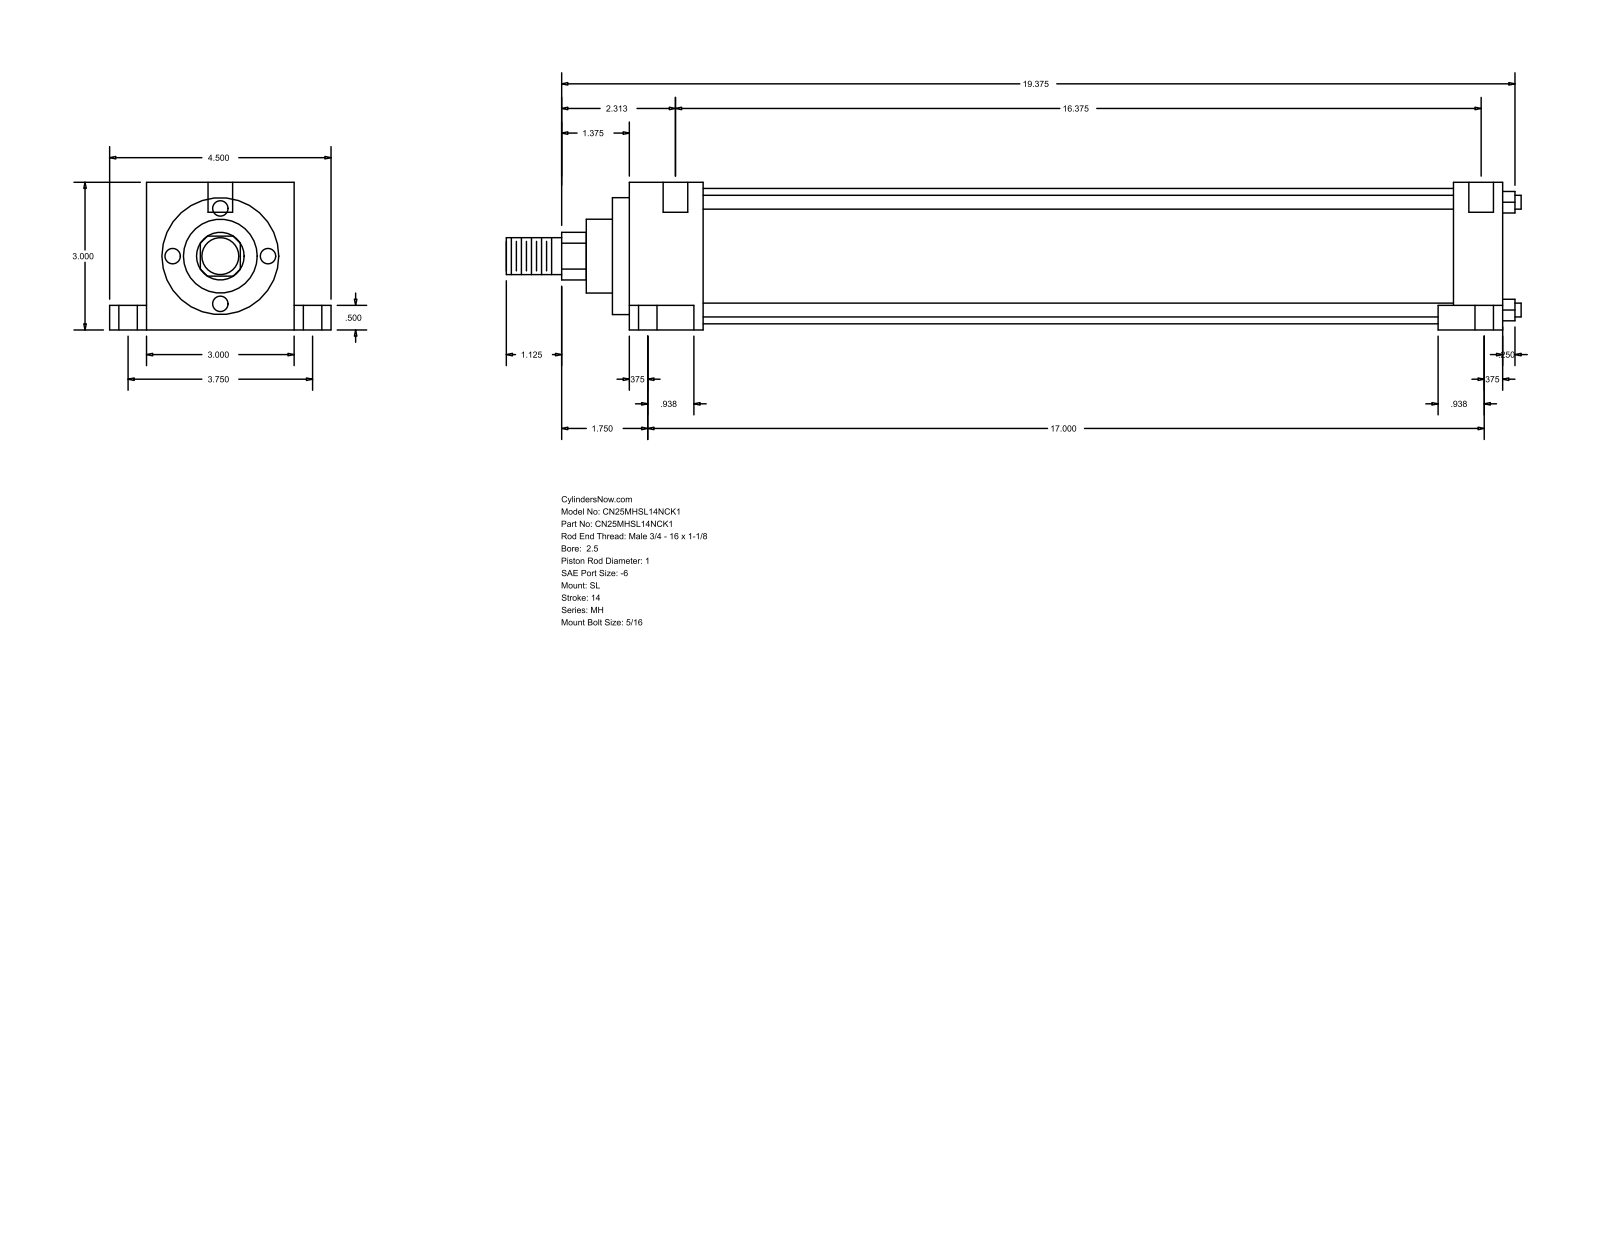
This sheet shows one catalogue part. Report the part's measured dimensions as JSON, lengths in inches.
{"part_name": "MH_SL__0250_1", "step_written_by": "GSSL Pune (CONFIG_CONTROL_DESIGN)", "units": "inches", "bodies": {"solids": 0, "faces": 86, "planar": 61, "cylindrical": 25, "other": 0}, "overall_size": [20.625, 4.5, 3], "round_holes": [[0.219, 2], [0.375, 2], [0.625, 2], [0.5, 1]], "round_bosses_or_shafts": [[0.281, 4], [2.75, 1], [2.375, 1], [1.5, 1], [1, 1], [0.75, 1]], "partial_cylinders_radius": [[0.484, 1]], "face_to_face_distances": [3, 1, 17.094, 18.094, 0.5, 2.5, 0.75, 3.75, 0.531, 17.625], "hole_center_spacings": [1.876, 0.125, 3.75]}
